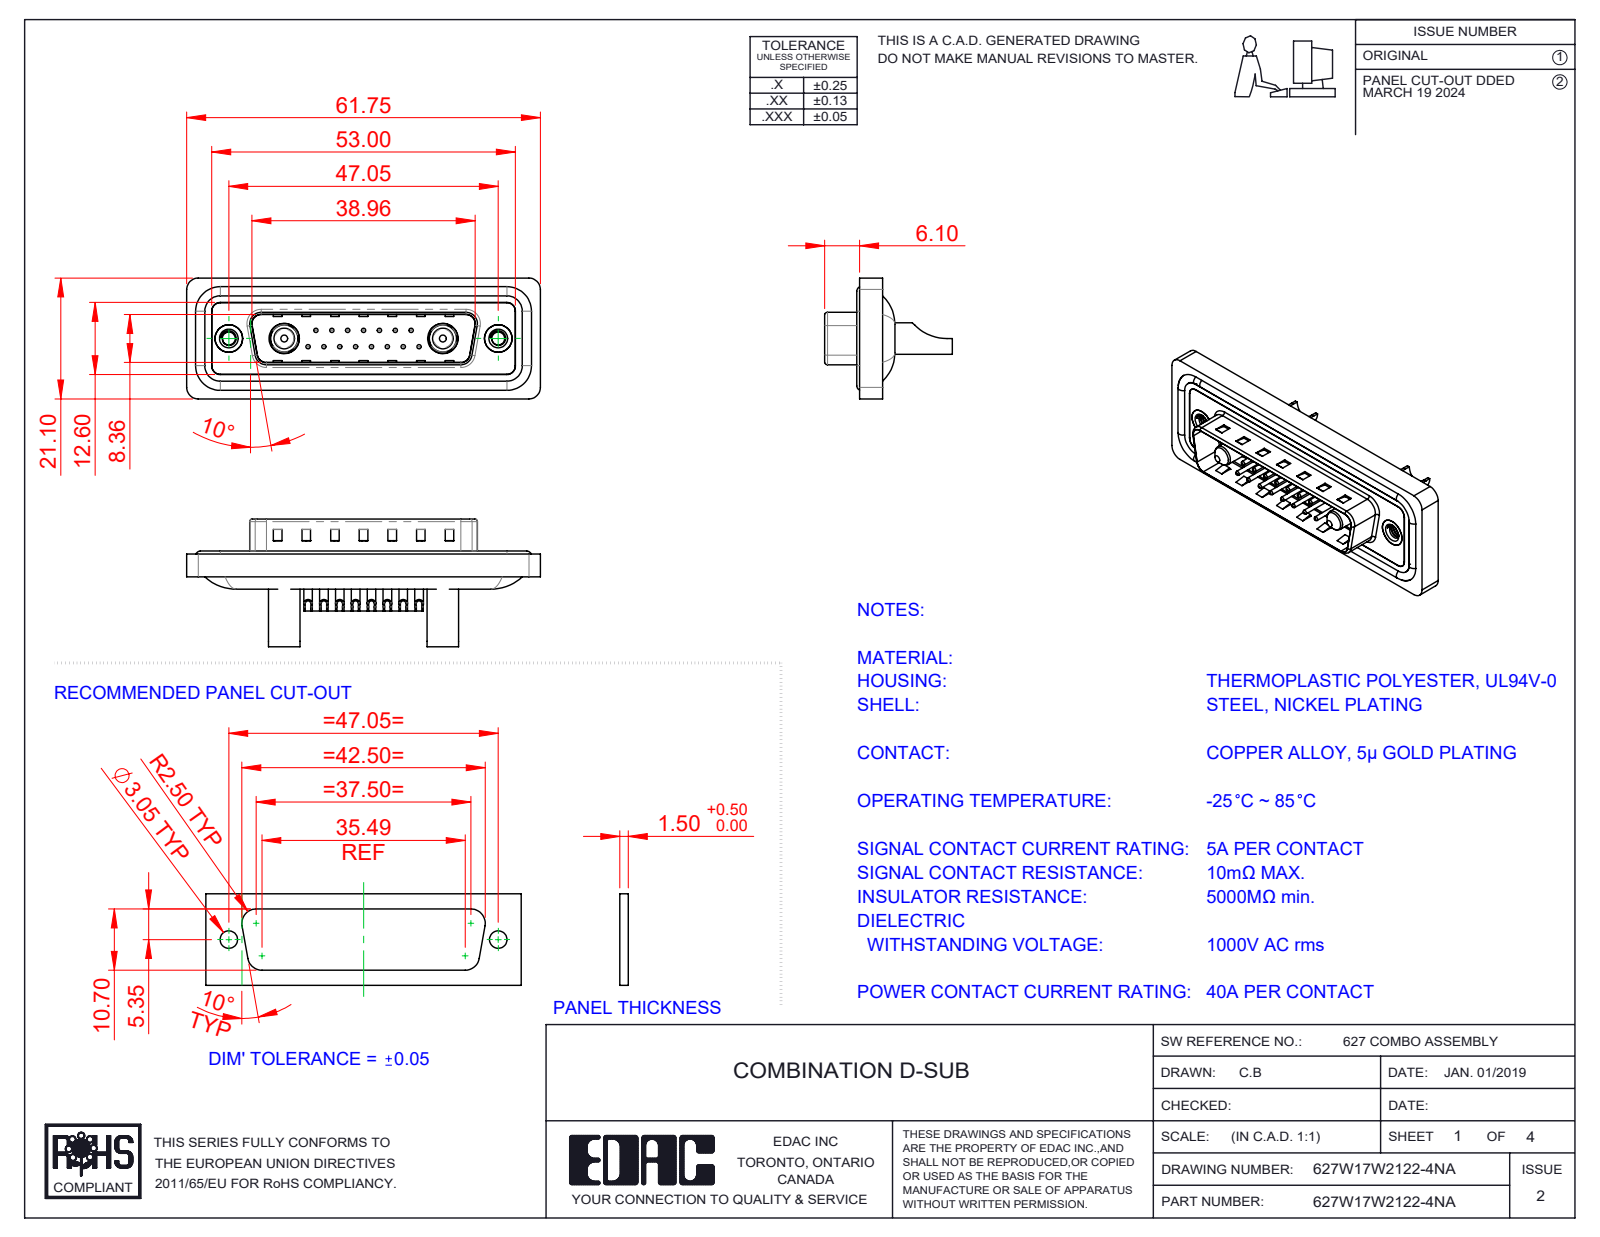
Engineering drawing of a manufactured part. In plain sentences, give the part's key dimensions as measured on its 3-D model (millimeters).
The part is named "627Combo Waterproof Housing_25 Contacts; 627Combo Threaded Rivet_A; 627Combo Contact Row 1_22; 627Combo Shell Front_25 Contacts (+5 more)". Its 3-D file was written by "SolidWorks 2023 (CONFIG_CONTROL_DESIGN)". It is 26 solids with 1120 faces: 368 planar, 470 cylindrical and 282 other. Overall it measures 61.75 by 22.3 by 21.1 millimeters. Its volume is 7 371 cubic millimeters and its surface area 12 311 square millimeters. Round holes: 15 of diameter 0.75, 15 of diameter 1, 15 of diameter 1.6, 15 of diameter 2, 2 of diameter 2.26, 2 of diameter 4, 2 of diameter 4.6, 2 of diameter 4.8, 2 of diameter 4.85, 2 of diameter 5, 2 of diameter 5.3. Round bosses or shafts: 15 of diameter 1.5, 4 of diameter 1.6, 2 of diameter 5.5, 2 of diameter 5.2, 2 of diameter 4.9, 2 of diameter 4.75, 2 of diameter 3.75, 2 of diameter 3.6. Partial cylindrical surfaces (rounded edges, fillets, slot ends): 22 of radius 1.5, 18 of radius 2, 8 of radius 0.5, 8 of radius 1.6, 6 of radius 1, 4 of radius 0.25, 4 of radius 0.6, 4 of radius 0.65. The main face-to-face distances are 0.4, 1.5, 1.1, 1.6, 0.5, 3.1, 2.9, 0.82, 9.58, 4.1. The hole center spacings are 3.16, 2.77, 5.54, 8.31, 5.04, 7.49, 11.08, 5.03.
